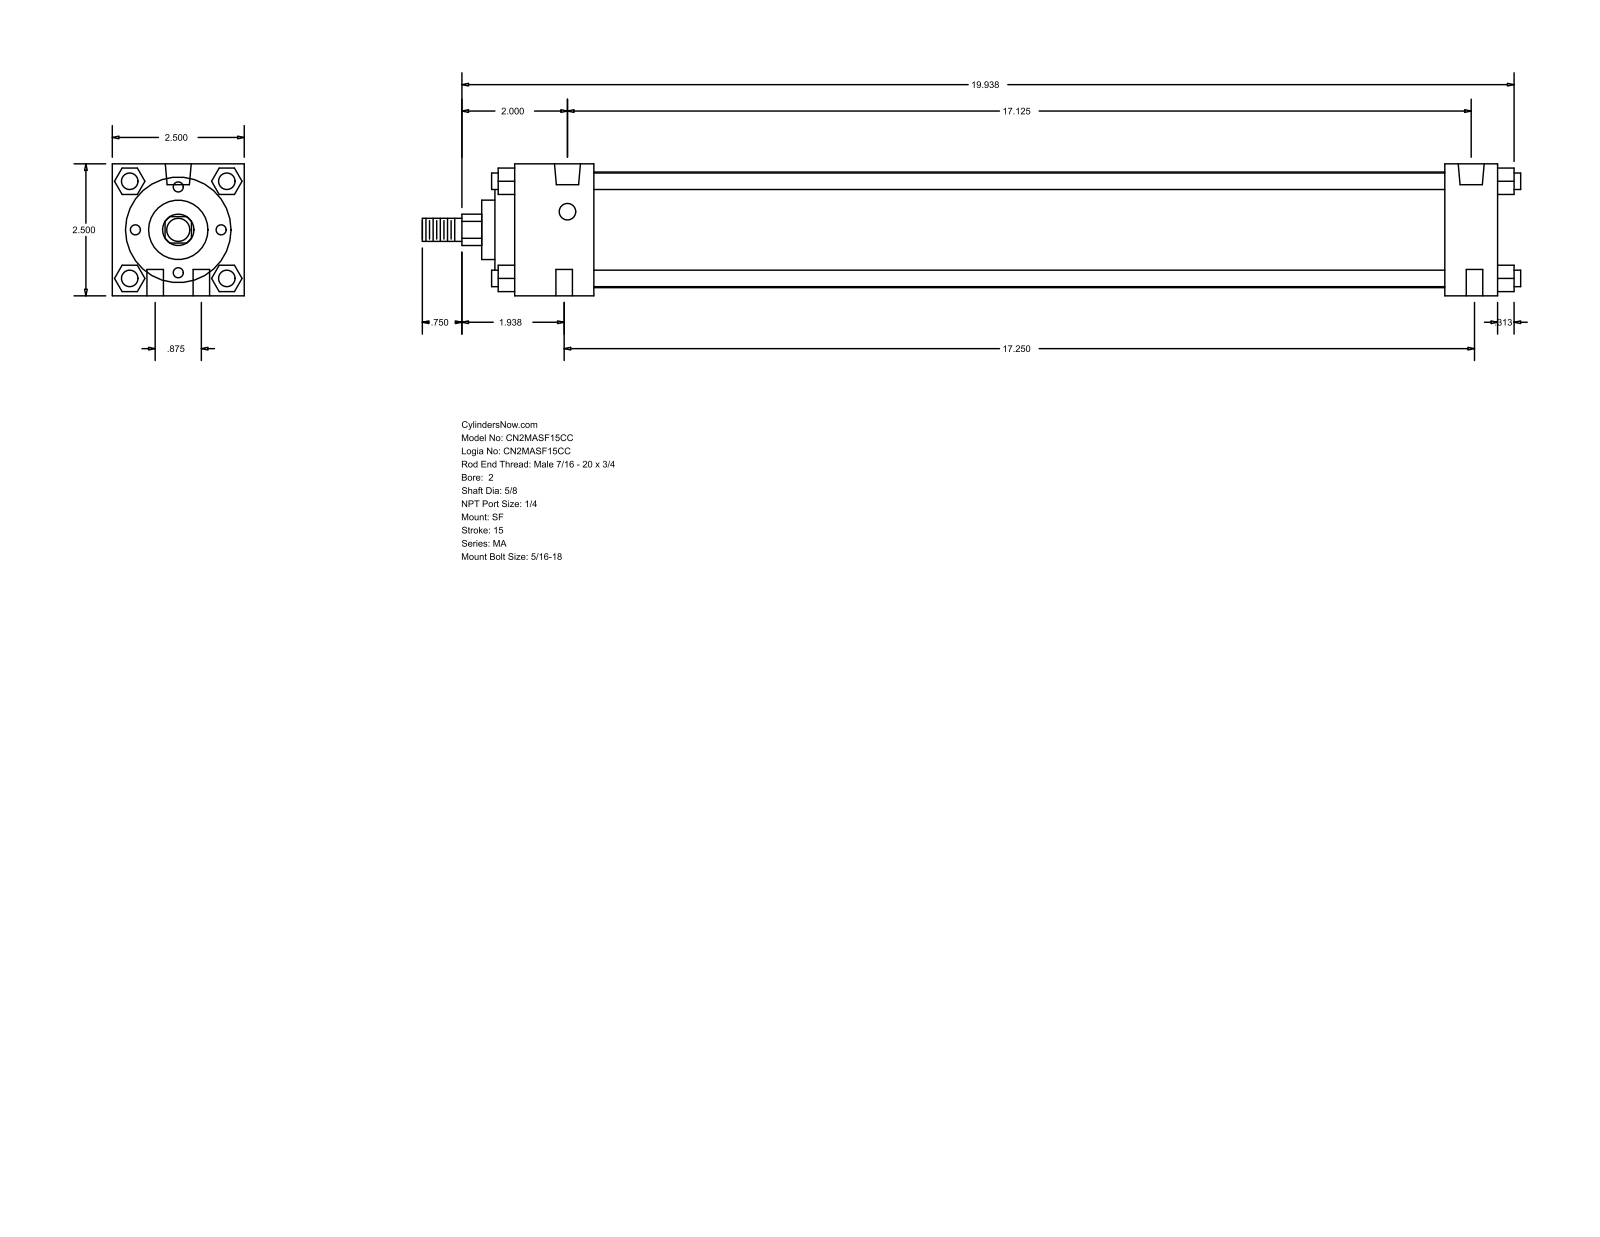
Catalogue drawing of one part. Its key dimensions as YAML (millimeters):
part_name: "MA_SF__0200_0.625"
step_written_by: "GSSL Pune (CONFIG_CONTROL_DESIGN)"
units: millimeters
bodies: {solids: 0, faces: 126, planar: 95, cylindrical: 31, other: 0}
overall_size: [528.64, 63.5, 63.5]
round_holes:
  - {diameter: 7.94, count: 6}
  - {diameter: 12.49, count: 2}
round_bosses_or_shafts:
  - {diameter: 7.94, count: 4}
  - {diameter: 55.63, count: 1}
  - {diameter: 50.8, count: 1}
  - {diameter: 28.57, count: 1}
  - {diameter: 15.88, count: 1}
  - {diameter: 11.11, count: 1}
partial_cylinders:
  - {radius: 7.54, count: 1}
face_to_face_distances: [63.5, 12.7, 38.1, 473.08, 447.67, 25.41, 409.57, 434.98, 9.52, 47.62]
hole_center_spacings: [11.22, 436.7, 22.22, 434.97, 438.15, 438.71]
